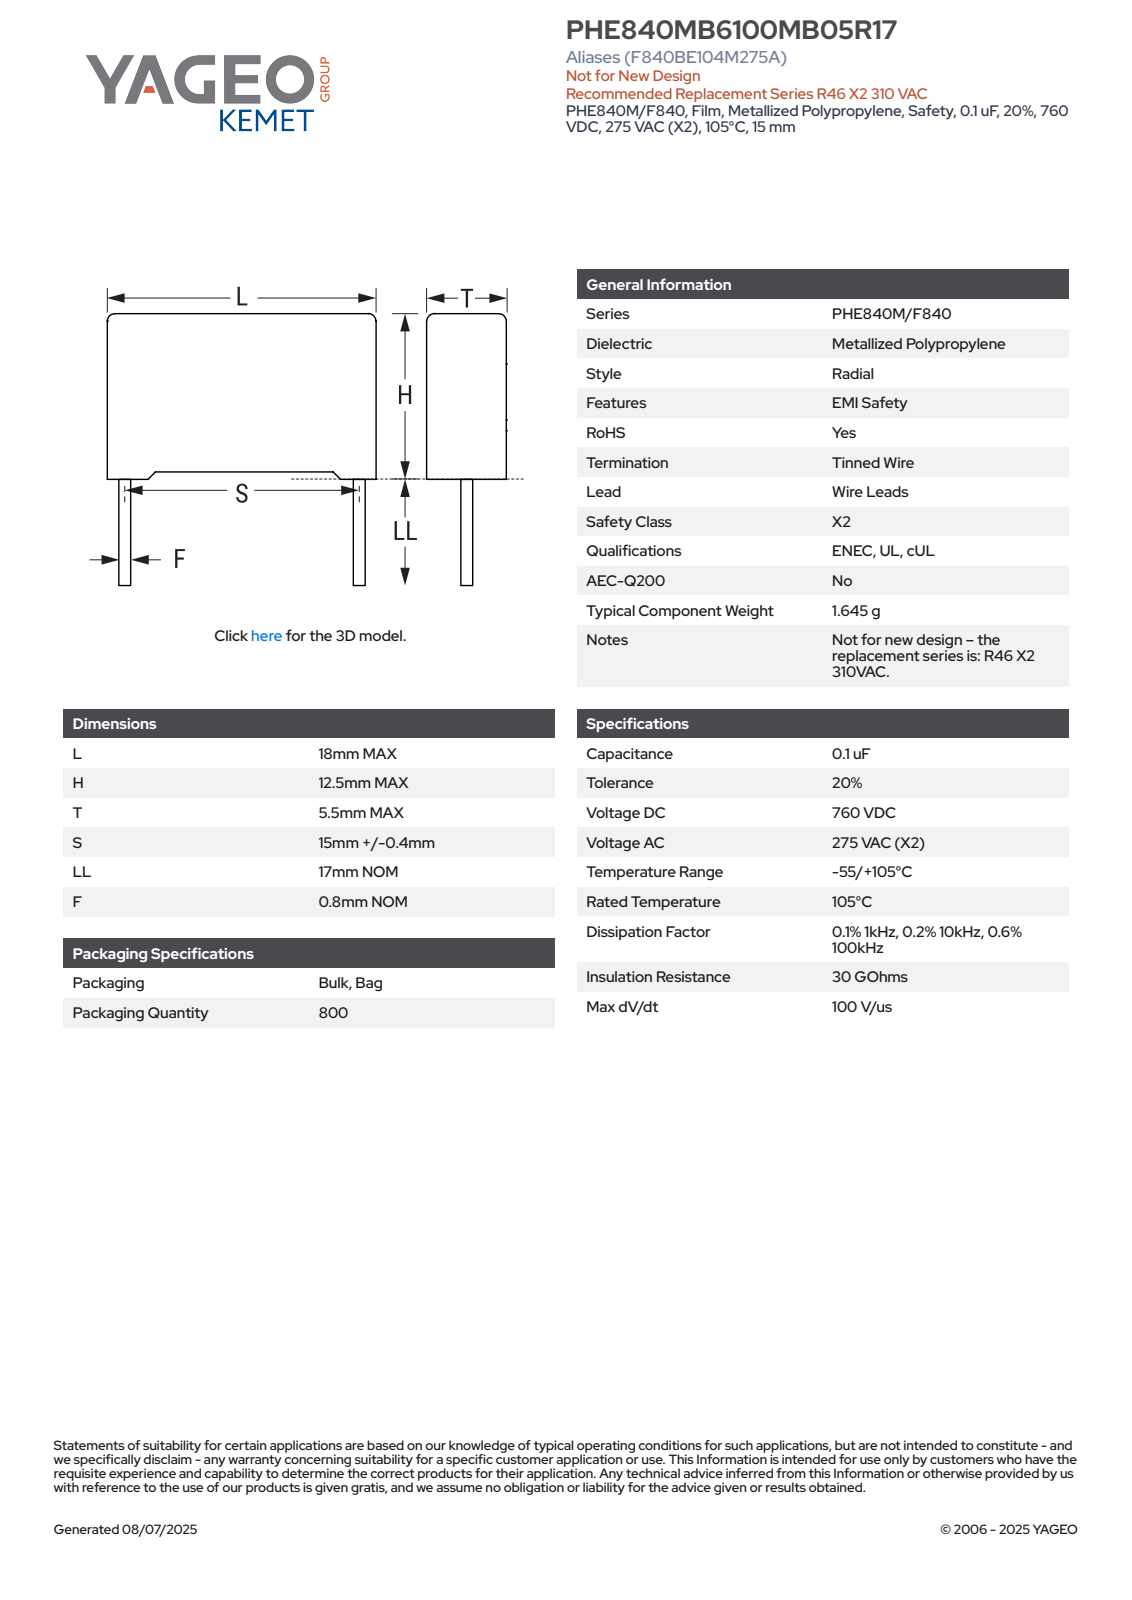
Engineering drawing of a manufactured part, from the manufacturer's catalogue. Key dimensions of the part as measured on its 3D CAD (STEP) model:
Part name (STEP PRODUCT): CFR_RB2_18X12.5X5.5_L18H12.5T5.5S15LL17F0.8
STEP written by: SolidWorks 2021 (AUTOMOTIVE_DESIGN)
Units: millimetres
Bodies: 4 solids, 85 faces (77 planar, 8 cylindrical, 0 other)
Overall size (bounding box): 29.5 × 18 × 5.5
Volume: 1 193 mm³ · Surface area: 901 mm²
Round bosses / shafts (diameter × count): ⌀0.8 ×2
Partial cylindrical surfaces — rounded edges, fillets, slot ends (radius × count): R0.5 ×4
Main face-to-face distances: 5.5, 11.75, 18, 0.6, 4.9, 0.32, 12.07, 0.75, 0.43, 12.5
